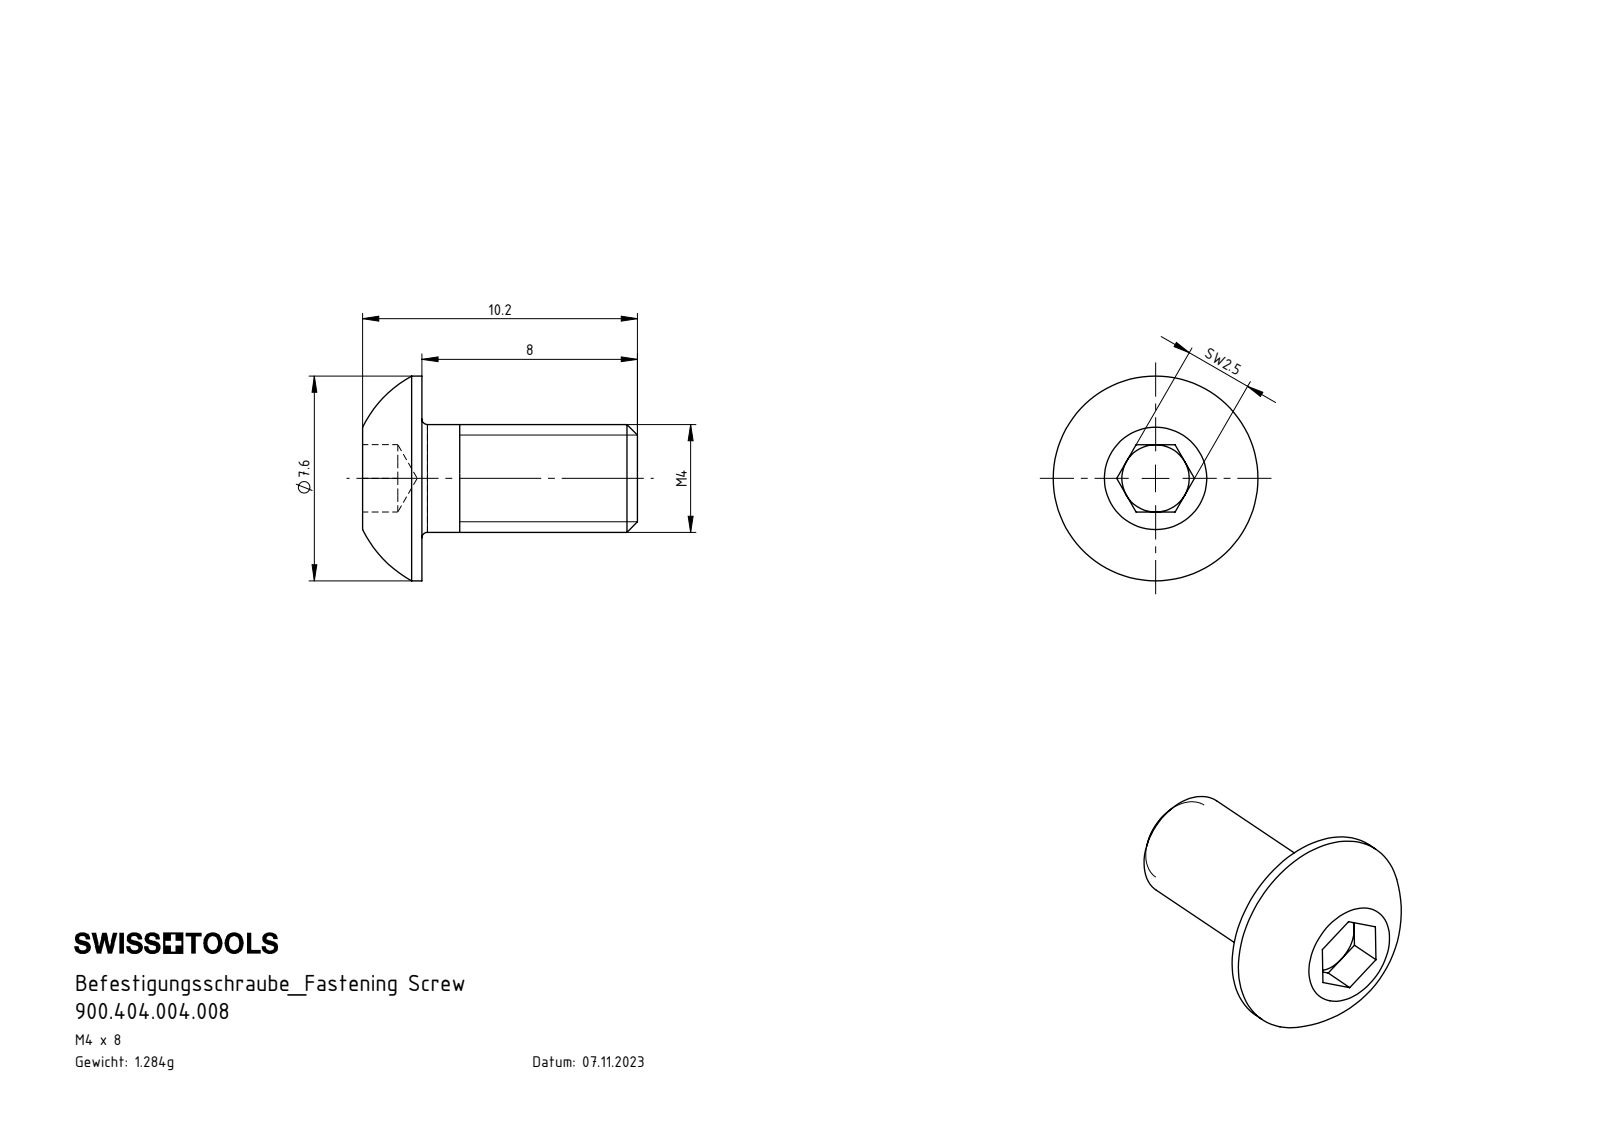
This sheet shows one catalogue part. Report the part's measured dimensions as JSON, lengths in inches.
{"part_name": "900.404.004.008", "step_written_by": "SolidWorks 2022 (AUTOMOTIVE_DESIGN)", "units": "inches", "bodies": {"solids": 1, "faces": 27, "planar": 15, "cylindrical": 4, "other": 8}, "overall_size": [0.402, 0.299, 0.299], "volume_in3": 0.01, "surface_area_in2": 0.347, "round_bosses_or_shafts": [[0.299, 1], [0.157, 1]], "face_to_face_distances": [0.315, 0.087, 0.402, 0.098, 0.051, 0.035, 0.35]}
